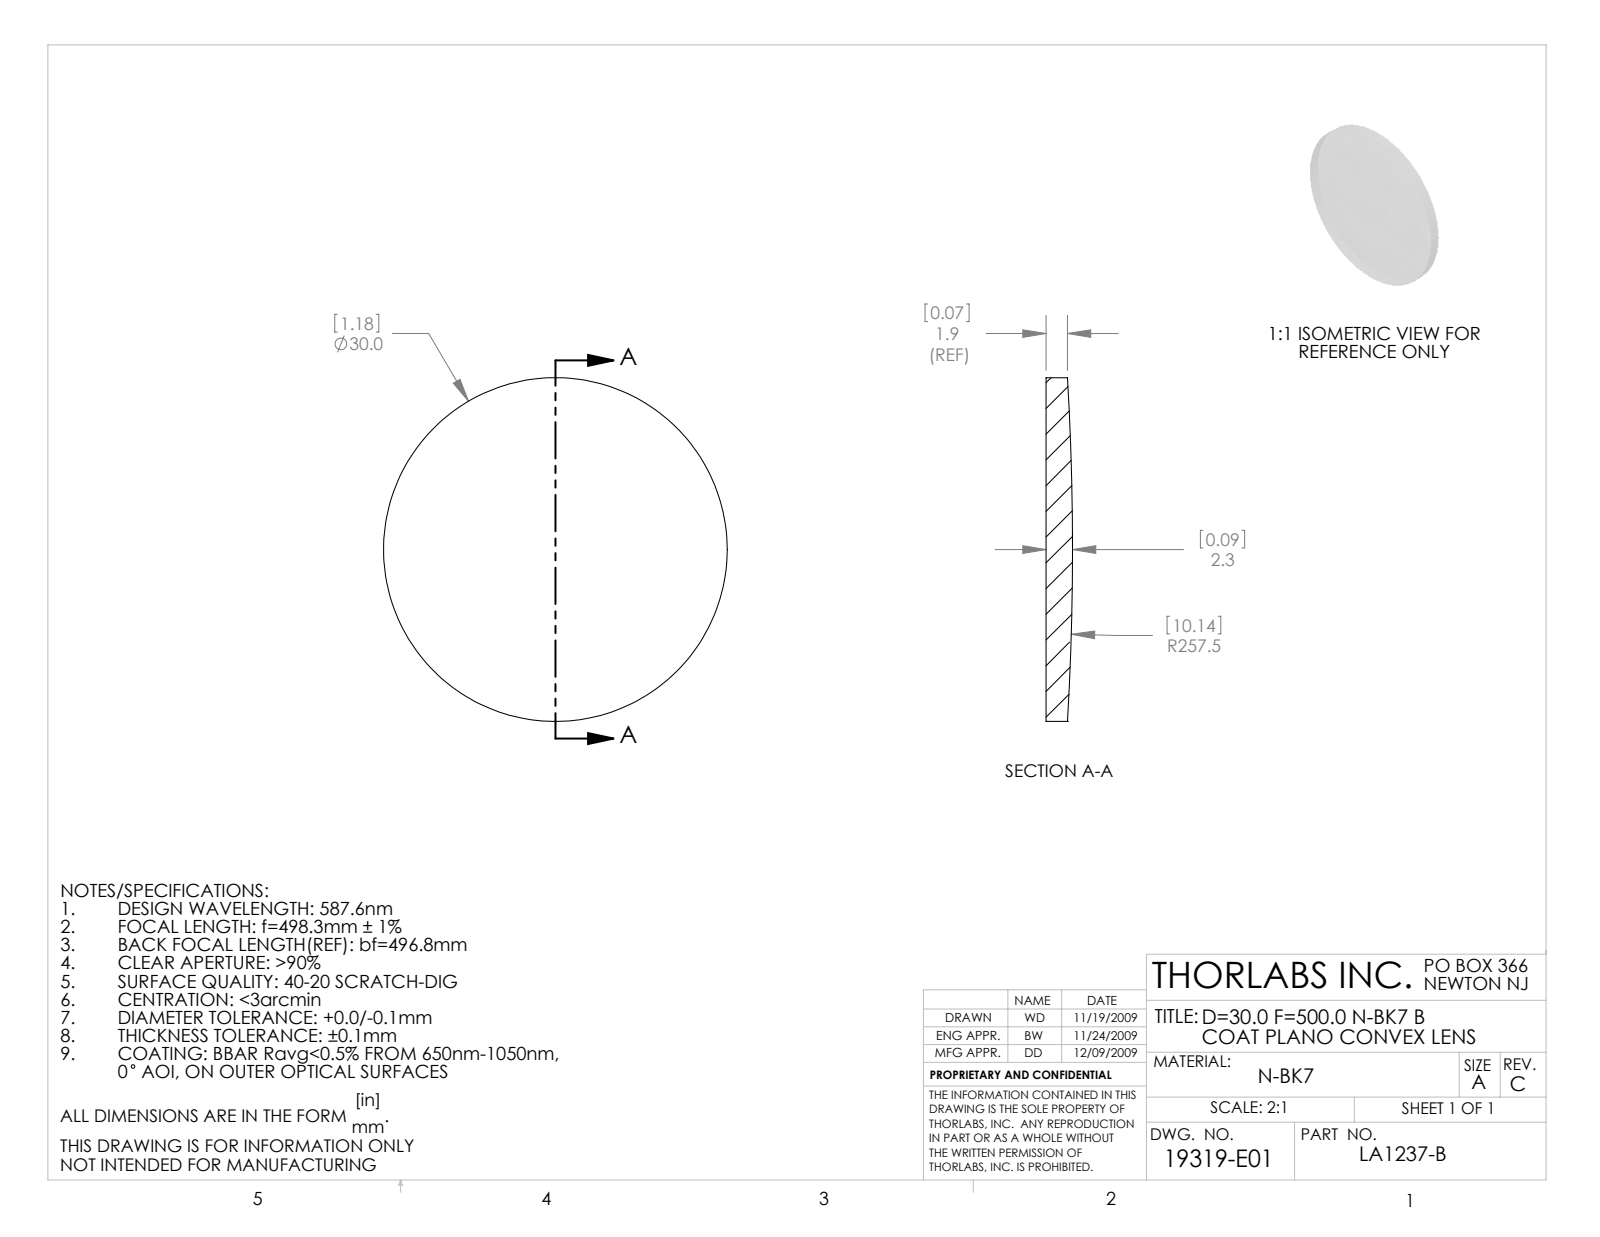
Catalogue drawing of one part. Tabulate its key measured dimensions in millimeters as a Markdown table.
| quantity | value |
| --- | --- |
| part name | 19319-E0W |
| STEP written by | SolidWorks 2009 (AUTOMOTIVE_DESIGN) |
| units | millimeters |
| bodies | 1 solid, 5 faces (1 planar, 2 cylindrical, 2 other) |
| overall size | 30 × 30 × 2.31 |
| volume | 1 478 mm³ |
| surface area | 1 591 mm² |
| round bosses / shafts (diameter × count) | 30 × 1 |
